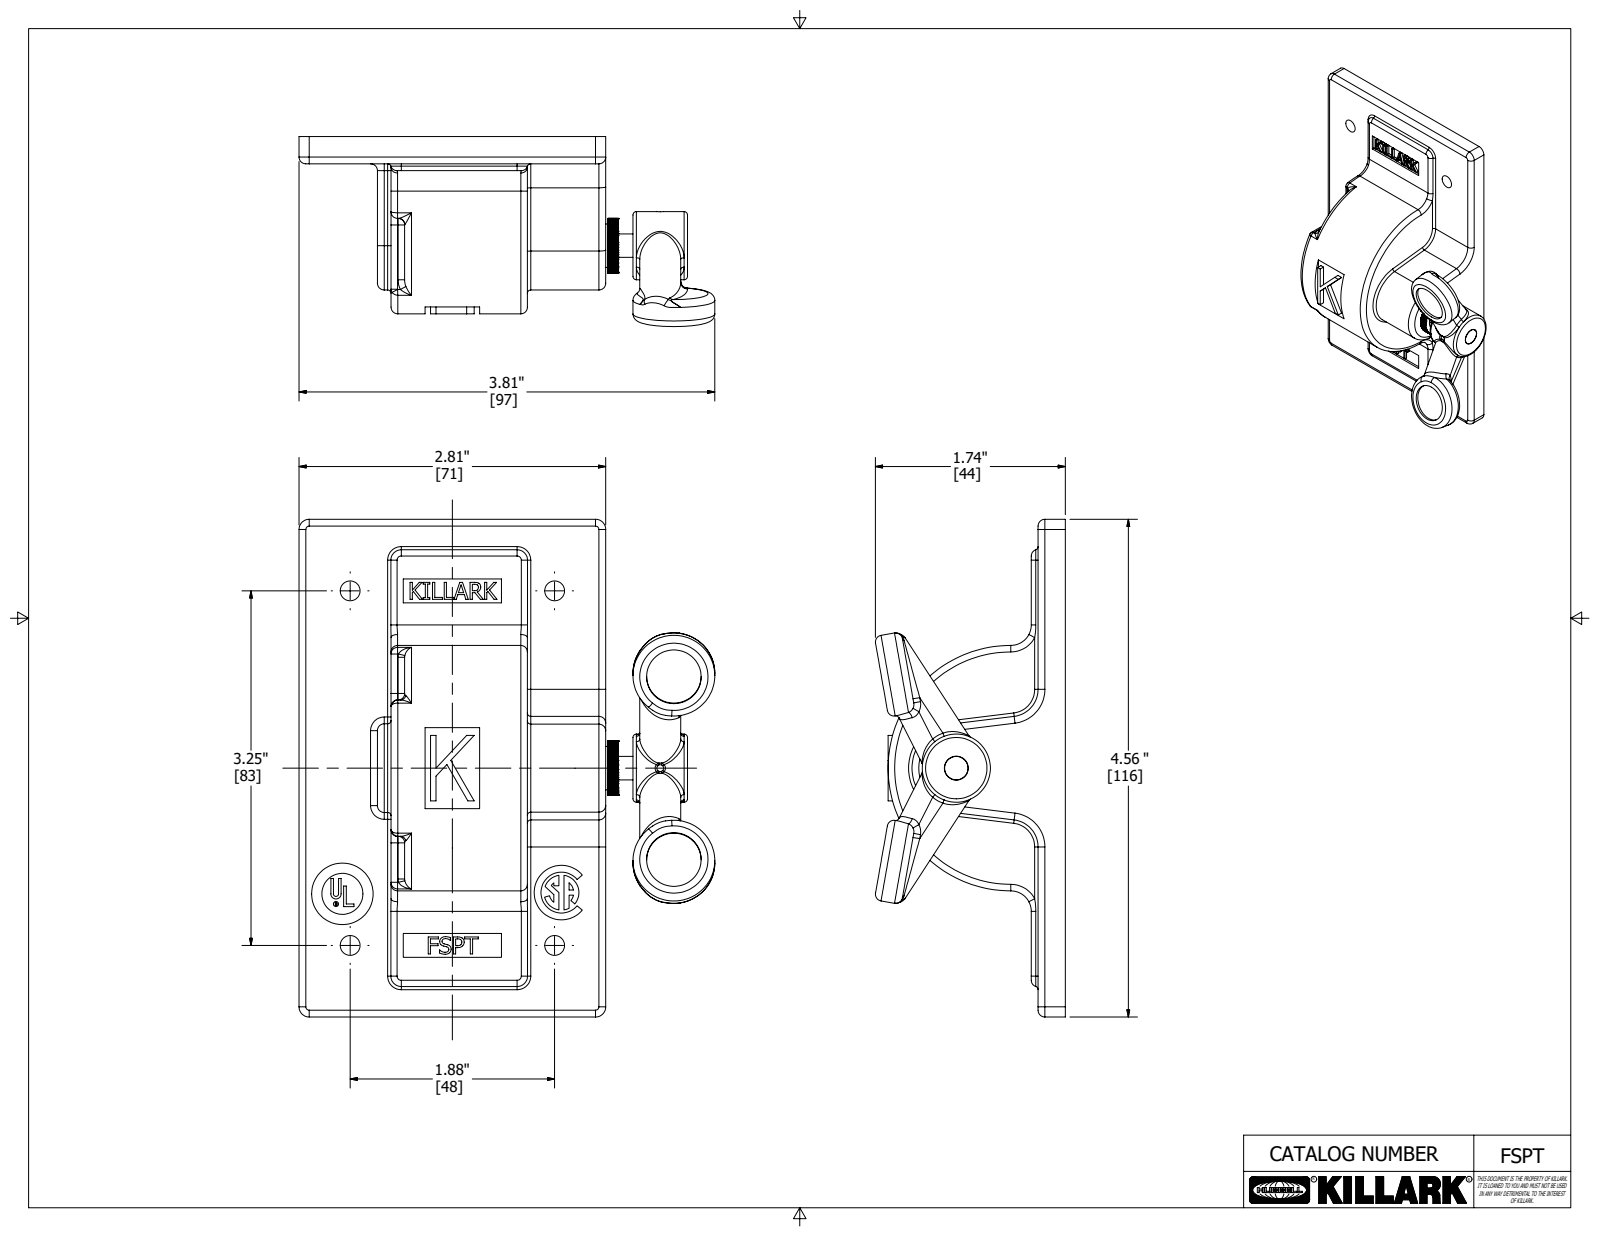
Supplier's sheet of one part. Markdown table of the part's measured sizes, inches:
| quantity | value |
| --- | --- |
| part name | KIL_FSPT; 0067534M; 0245924C; 0700405B (+2 more) |
| STEP written by | Autodesk Inventor 2020 (AUTOMOTIVE_DESIGN) |
| units | inches |
| bodies | 6 solids, 4074 faces (2860 planar, 699 cylindrical, 515 other) |
| overall size | 4.563 × 3.813 × 1.932 |
| volume | 4.83 in³ |
| surface area | 58.71 in² |
| round holes (diameter × count) | 0.133 × 4, 0.182 × 4, 0.5 × 2, 0.047 × 1, 0.067 × 1, 0.22 × 1, 0.257 × 1, 0.318 × 1, 0.359 × 1, 0.564 × 1 |
| round bosses / shafts (diameter × count) | 0.75 × 2, 0.097 × 2, 0.625 × 1, 0.5 × 1, 0.397 × 1, 0.376 × 1, 0.373 × 1, 0.25 × 1 |
| partial cylindrical surfaces (radius × count) | 0.031 × 22, 0.125 × 22, 0.062 × 17, 0.06 × 12, 0.105 × 10, 0.187 × 10, 0.094 × 4, 0.25 × 3 |
| main face-to-face distances | 0.25, 0.125, 0.125, 0.063, 0.719, 2.094, 0.313, 0.188, 1.969, 1.093 |
| hole center spacings | 0.217, 1.875, 3.25, 3.752, 0.11, 0.319, 0.351, 0.375 |
